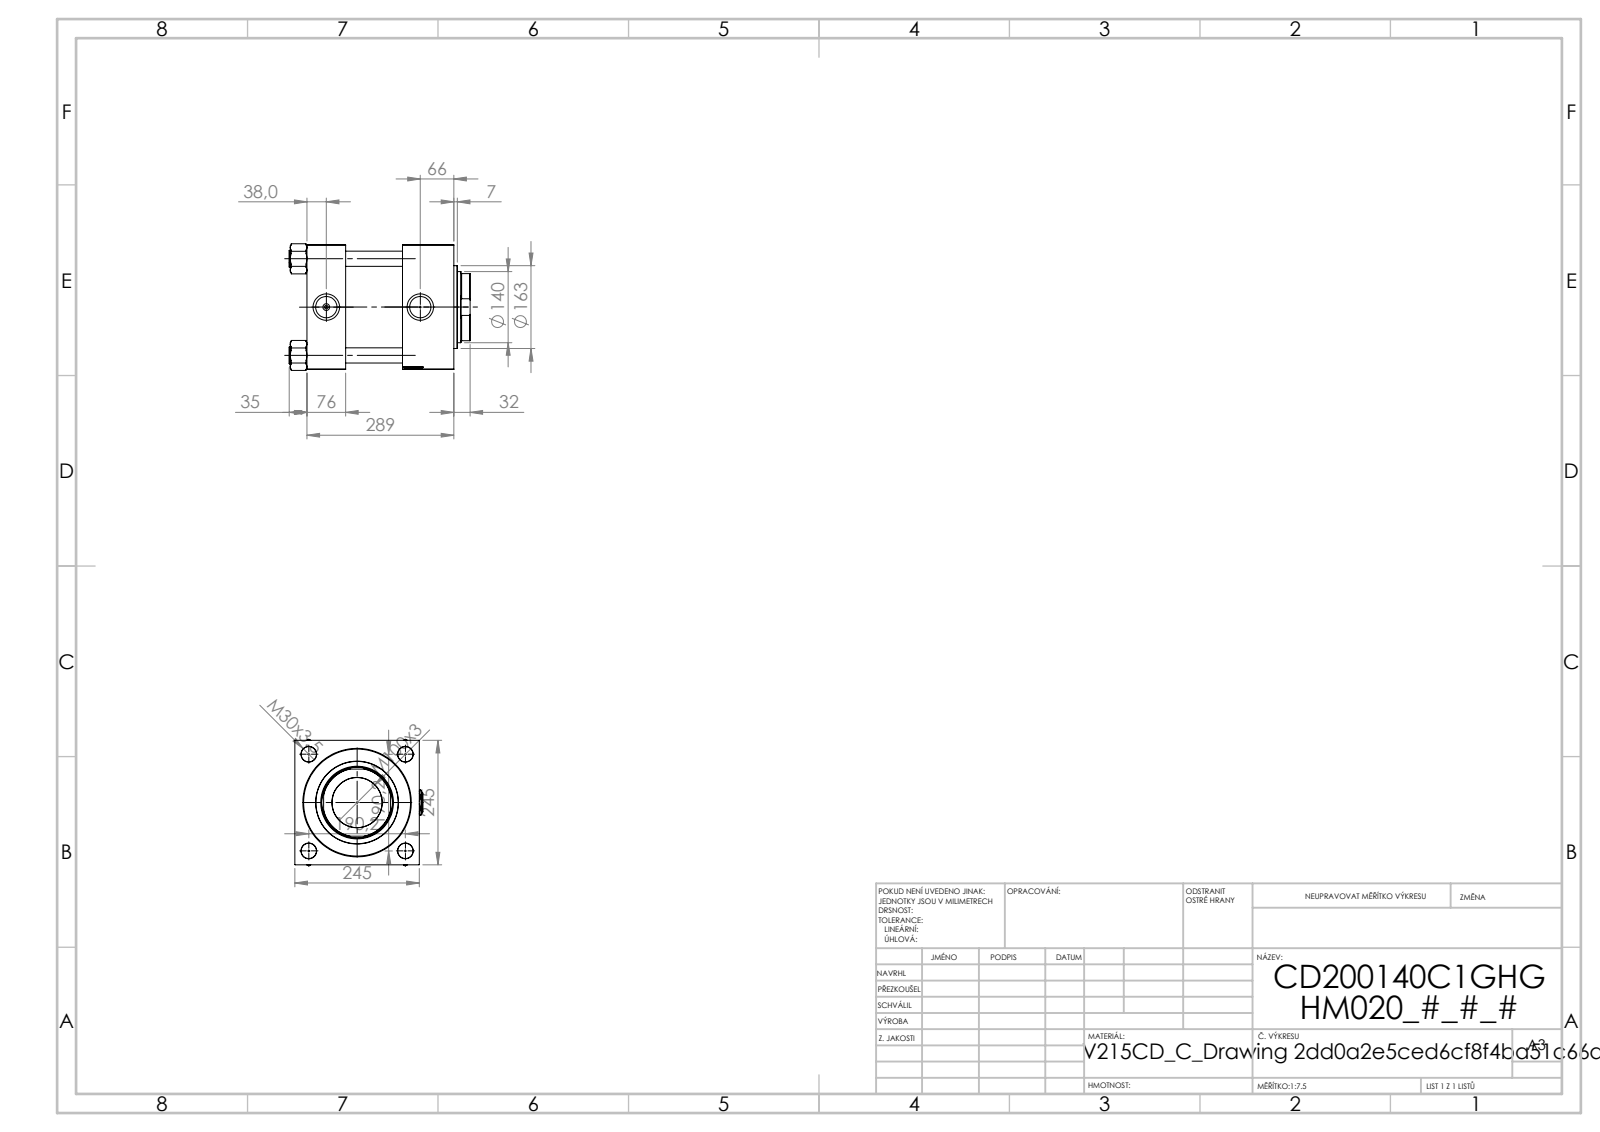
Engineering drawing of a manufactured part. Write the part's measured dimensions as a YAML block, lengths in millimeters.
part_name: "NUT_M5_V215CD_C; V215CD_VC_C; V215CD_VCP_C; V215CD_C_TYCINKA (+2 more)"
step_written_by: "SolidWorks 2019 (CONFIG_CONTROL_DESIGN)"
units: millimeters
bodies: {solids: 12, faces: 1243, planar: 597, cylindrical: 90, other: 556}
overall_size: [356, 252, 249.44]
volume: 13840000
surface_area: 1079000
round_holes:
  - {diameter: 30, count: 4}
  - {diameter: 7, count: 2}
  - {diameter: 41.92, count: 2}
  - {diameter: 52, count: 2}
  - {diameter: 98.5, count: 1}
  - {diameter: 140, count: 1}
  - {diameter: 143, count: 1}
  - {diameter: 146, count: 1}
  - {diameter: 200, count: 1}
  - {diameter: 210.5, count: 1}
round_bosses_or_shafts:
  - {diameter: 33, count: 4}
  - {diameter: 206, count: 1}
  - {diameter: 163, count: 1}
partial_cylinders:
  - {radius: 68, count: 1}
face_to_face_distances: [245, 76, 188, 112, 260.3, 184.3, 72.3, 289, 213, 101]
hole_center_spacings: [134.49, 190.2, 268.98, 185]
